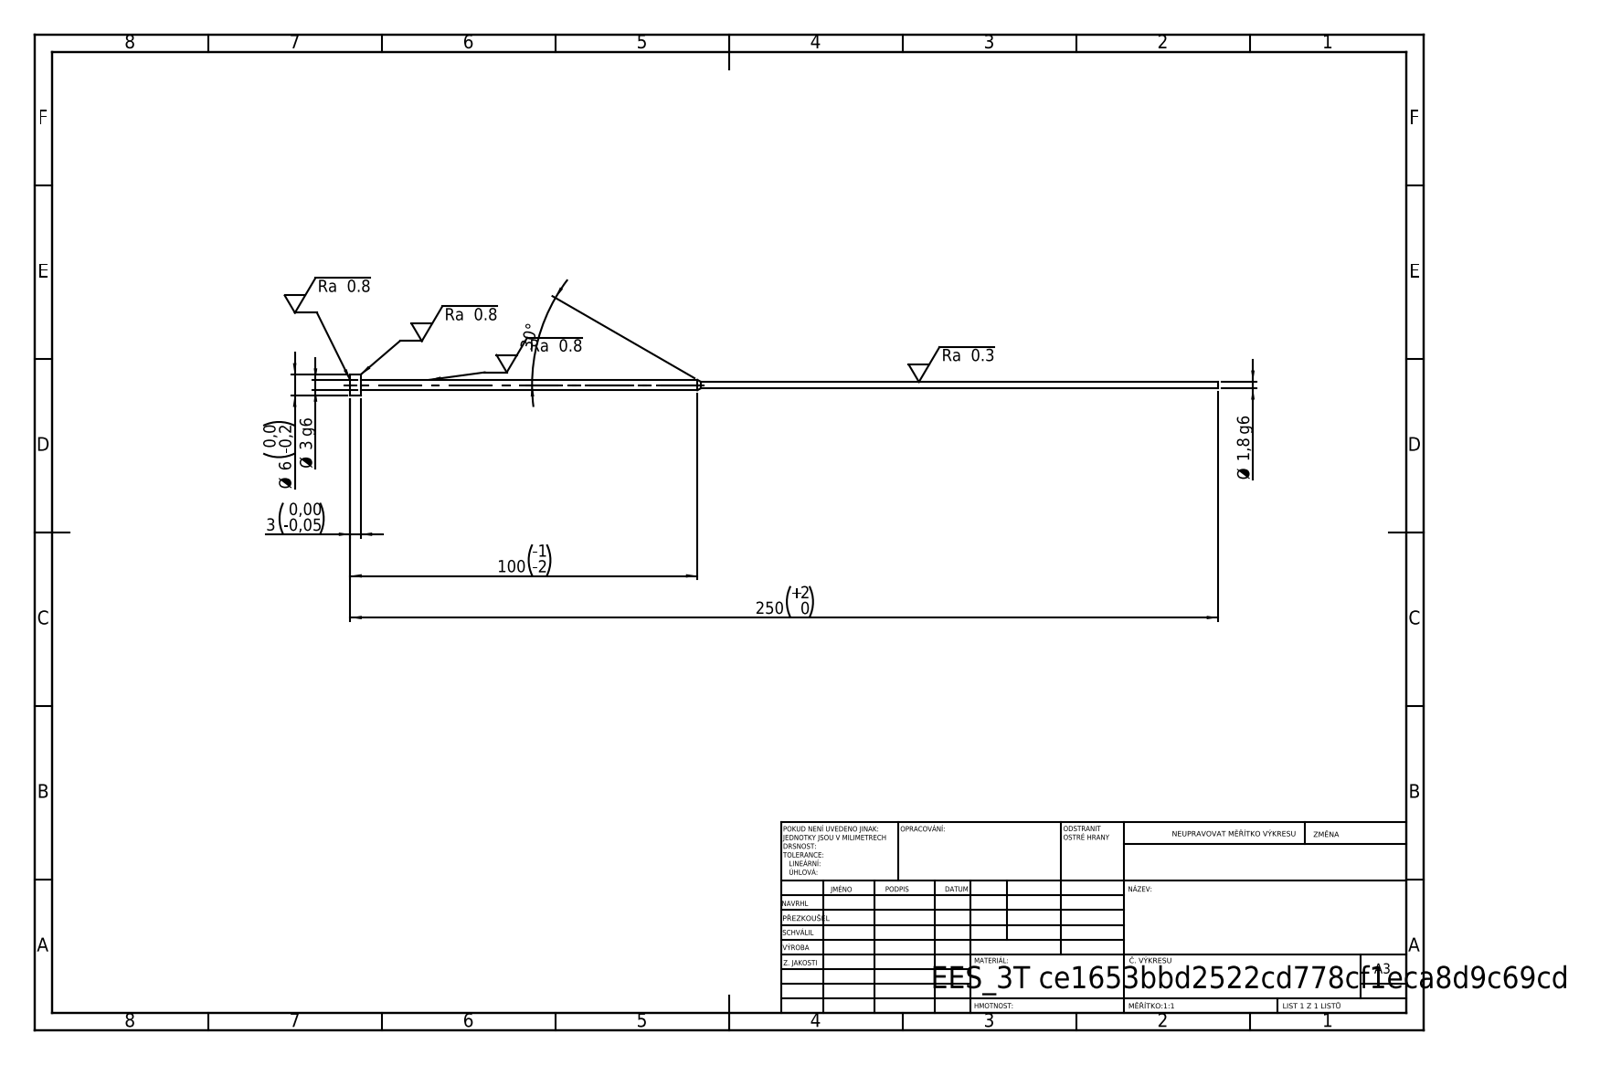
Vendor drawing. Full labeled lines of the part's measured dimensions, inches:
STEP written by: SolidWorks 2019 (CONFIG_CONTROL_DESIGN)
Units: inches
Bodies: 1 solid, 11 faces (3 planar, 6 cylindrical, 2 other)
Overall size (bounding box): 9.843 × 0.236 × 0.236
Volume: 0.07 in³ · Surface area: 2.905 in²
Round bosses / shafts (diameter × count): ⌀0.236 ×1, ⌀0.118 ×1, ⌀0.071 ×1
Main face-to-face distances: 0.118, 9.724, 9.843
